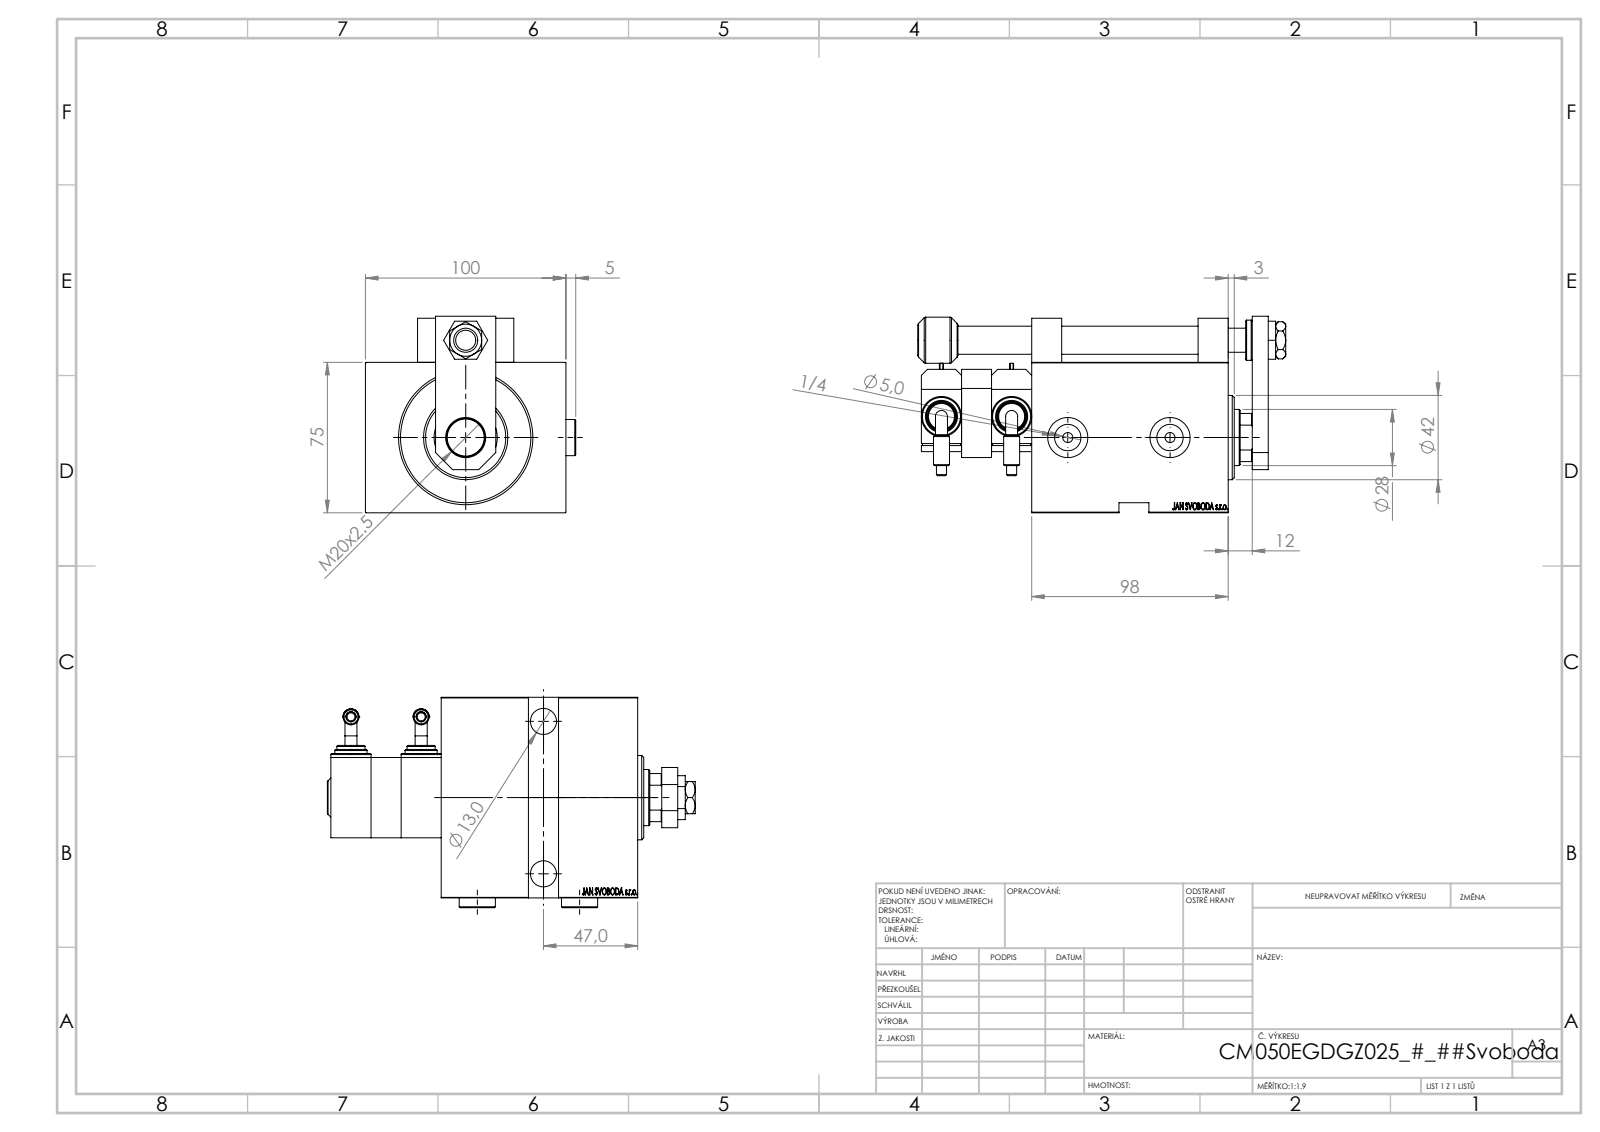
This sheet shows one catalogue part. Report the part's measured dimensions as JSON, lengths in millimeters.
{"part_name": "SWITCH DIM W_B; Zatka_OIL_PORT; MIDDLE; KROUZEK_PRO_TYC (+7 more)", "step_written_by": "SolidWorks 2019 (CONFIG_CONTROL_DESIGN)", "units": "millimeters", "bodies": {"solids": 16, "faces": 1155, "planar": 560, "cylindrical": 126, "other": 469}, "overall_size": [183.5, 104.9, 98], "volume_mm3": 826721, "surface_area_mm2": 149009, "round_holes": [[4, 4], [8, 4], [13, 3], [20, 3], [5, 2], [13.16, 2], [19, 2], [12, 1], [14, 1], [18.5, 1], [28, 1], [31.5, 1]], "round_bosses_or_shafts": [[20, 3], [18, 2], [16, 2], [14, 2], [8, 2], [6, 2], [5.04, 2], [52, 1]], "partial_cylinders_radius": [[3, 1], [13.5, 1]], "face_to_face_distances": [35, 75, 5, 98, 20, 100, 118, 15, 70, 30], "hole_center_spacings": [20, 48.42, 51.73, 62.16, 64.78, 83, 85.38, 48.5]}
